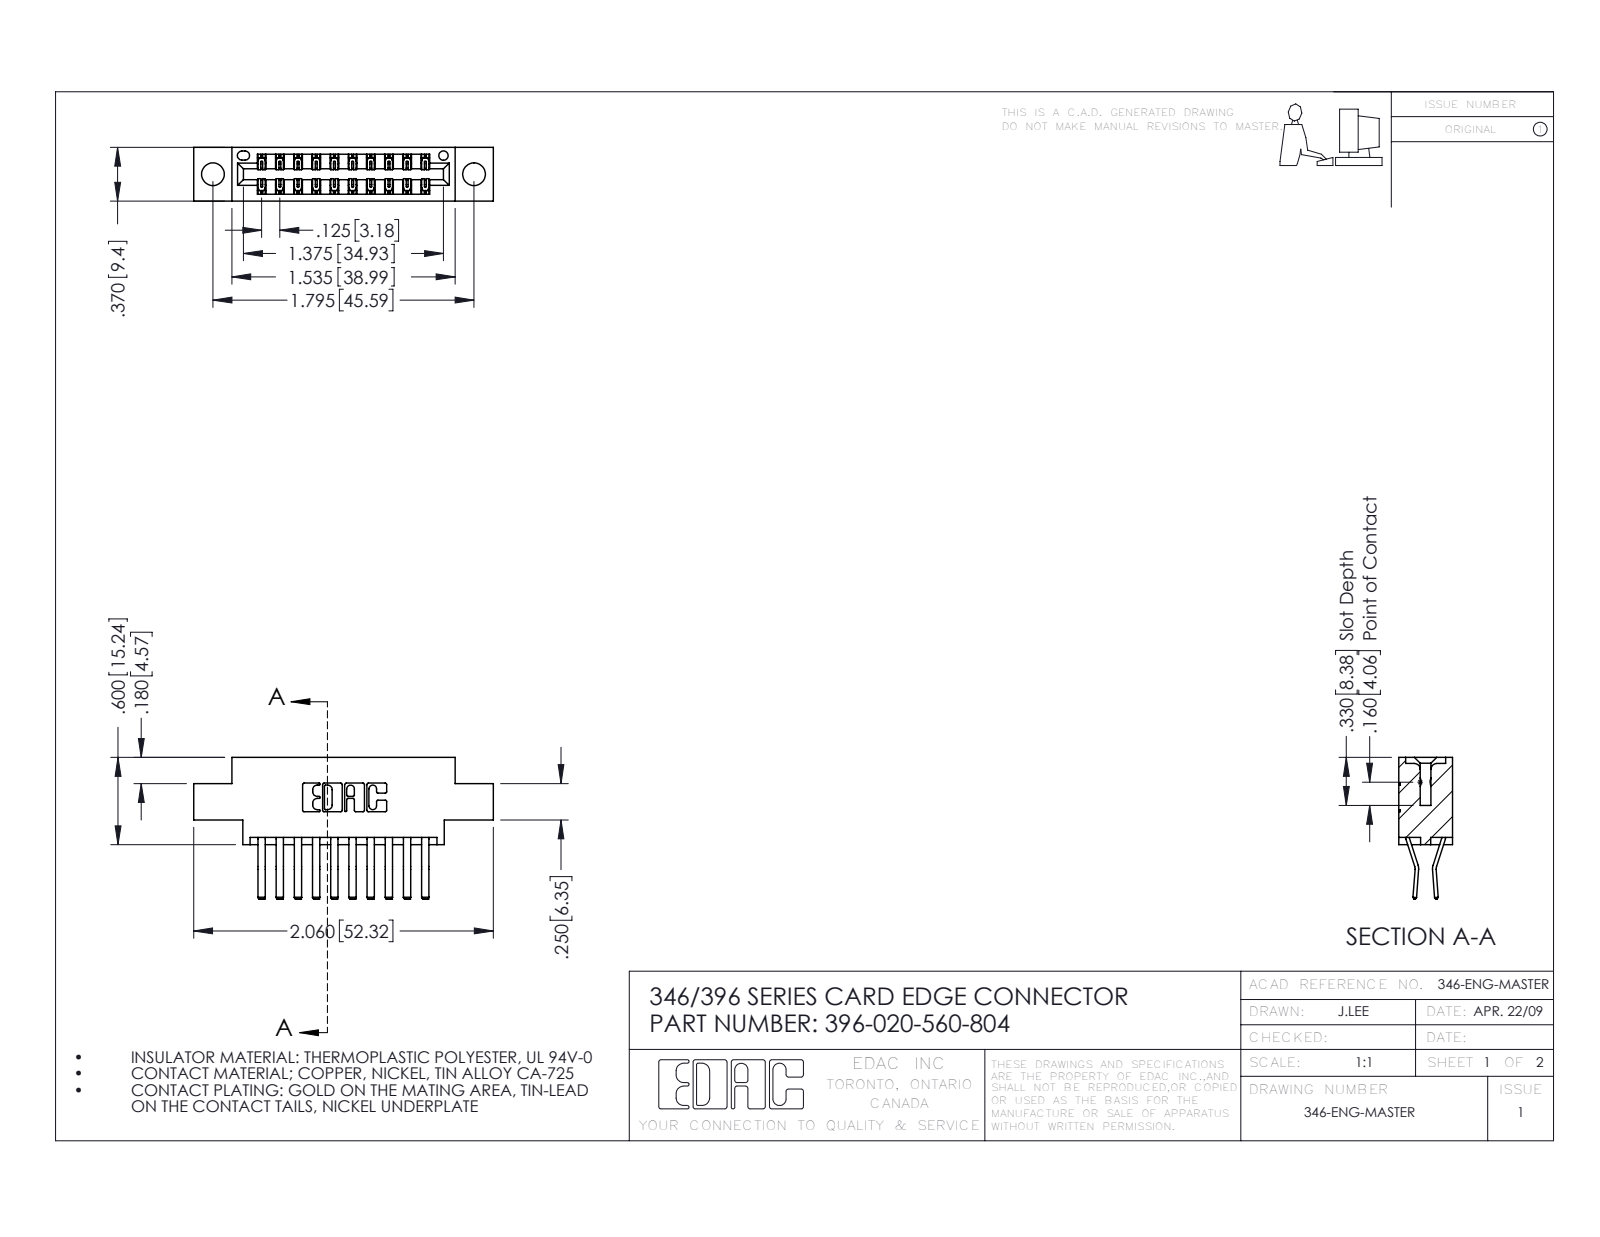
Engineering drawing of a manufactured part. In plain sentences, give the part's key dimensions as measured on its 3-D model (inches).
The part is named "346 Part_0.170 Offset - 0.156 Dia-TH; 345-292-001_560 Tail; 396-020-560-804". Its 3-D file was written by "SolidWorks 2016 (CONFIG_CONTROL_DESIGN)". It is 21 solids with 1206 faces: 780 planar, 426 cylindrical and 0 other. Overall it measures 2.06 by 0.975 by 0.37 inches. Its volume is 0.289 cubic inches and its surface area 9.856 square inches. Round holes: 2 of diameter 0.156, 1 of diameter 0.064. Partial cylindrical surfaces (rounded edges, fillets, slot ends): 30 of radius 0.006, 22 of radius 0.01, 6 of radius 0.007, 6 of radius 0.031, 3 of radius 0.026, 2 of radius 0.01, 2 of radius 0.014, 2 of radius 0.022. The main face-to-face distances are 0.25, 0.37, 0.048, 0.322, 0.025, 0.072, 0.298, 0.275, 0.148, 0.222. The hole center spacings are 0.246, 1.59, 1.795.
